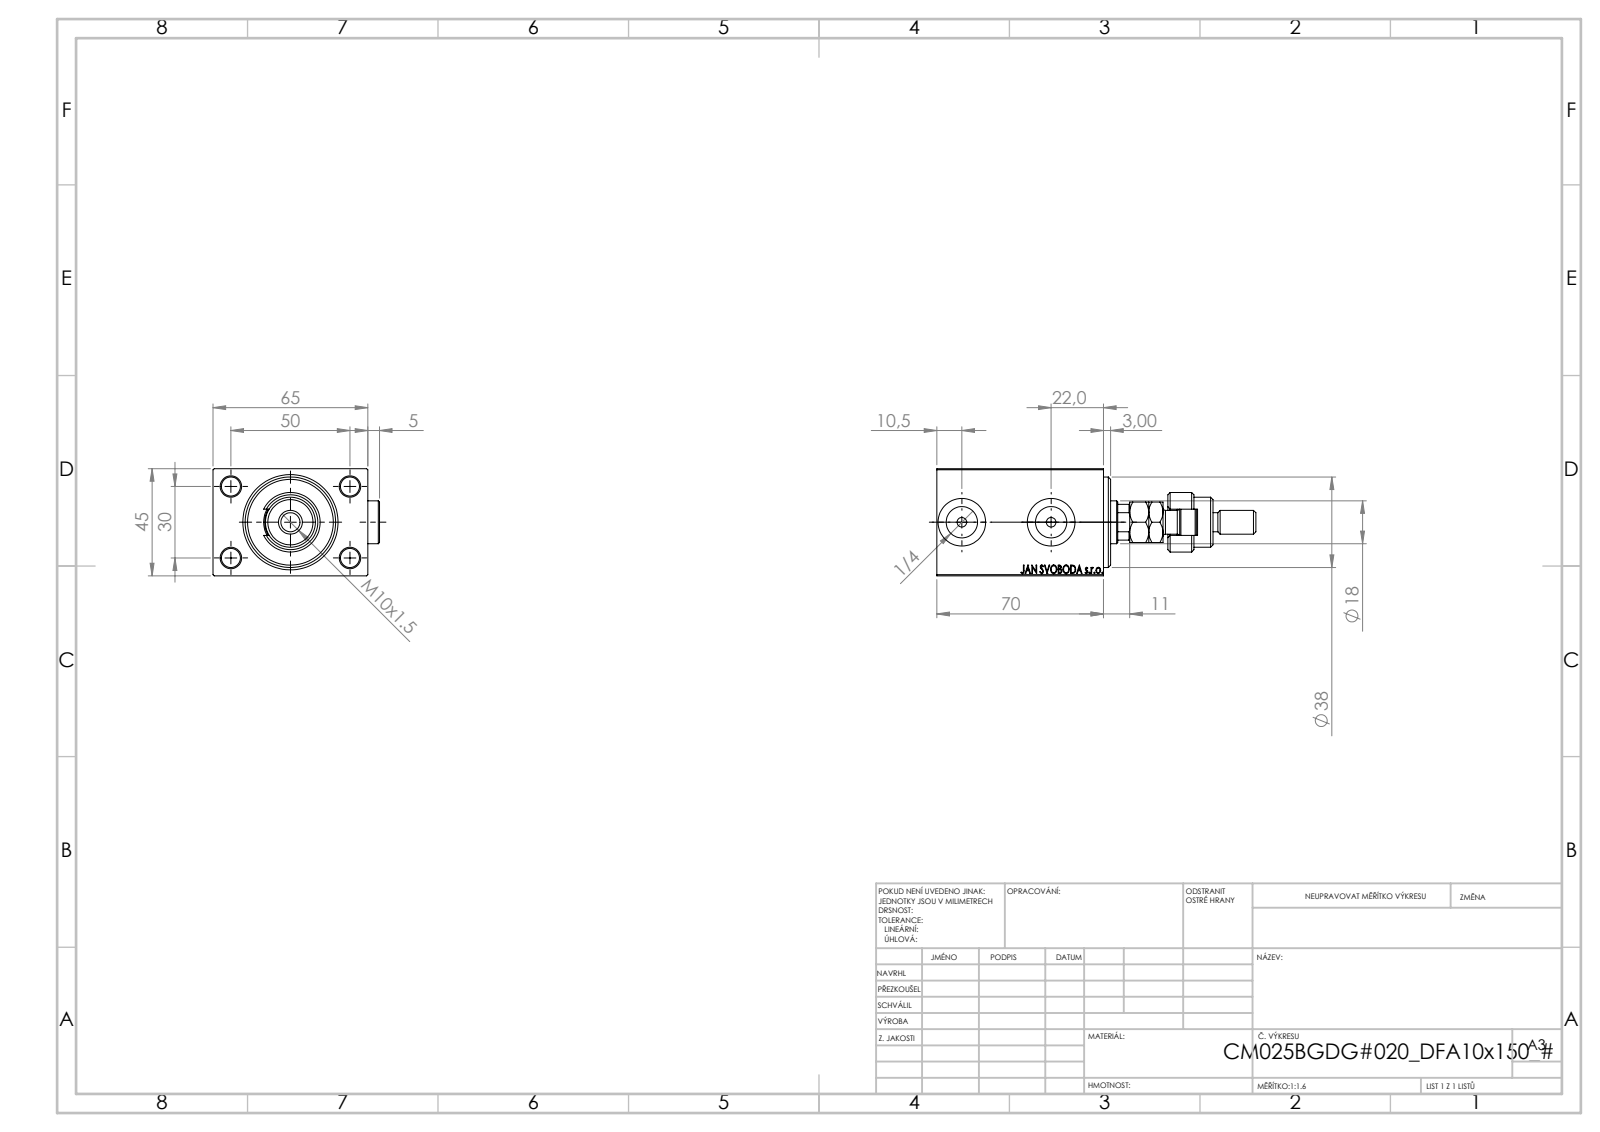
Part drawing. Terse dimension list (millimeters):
name: V450CM_B_VCP; V450CM_B_Body; FEMALE_PART_FOR_DFA; MFA (+2 more)
written by: SolidWorks 2019 (CONFIG_CONTROL_DESIGN)
unit: mm
bodies: 7 solids, 1020 faces (463 planar, 83 cylindrical, 474 other)
size: 134 × 69.9 × 45
volume: 204 140 mm³; area: 49 354 mm²
holes: 4× ⌀8, 2× ⌀4, 2× ⌀13.16, 2× ⌀20, 1× ⌀8.5, 1× ⌀18, 1× ⌀21.5, 1× ⌀22.5, 1× ⌀27, 1× ⌀38
bosses: 2× ⌀18, 1× ⌀25, 1× ⌀21, 1× ⌀16, 1× ⌀10, 1× ⌀8
rounds: 1× R5.5, 1× R8.5, 1× R8.75
face distances: 45, 65, 5, 70, 6, 59, 64.9, 14, 64, 8
hole spacings: 29.15, 30, 50, 58.31, 37.5
